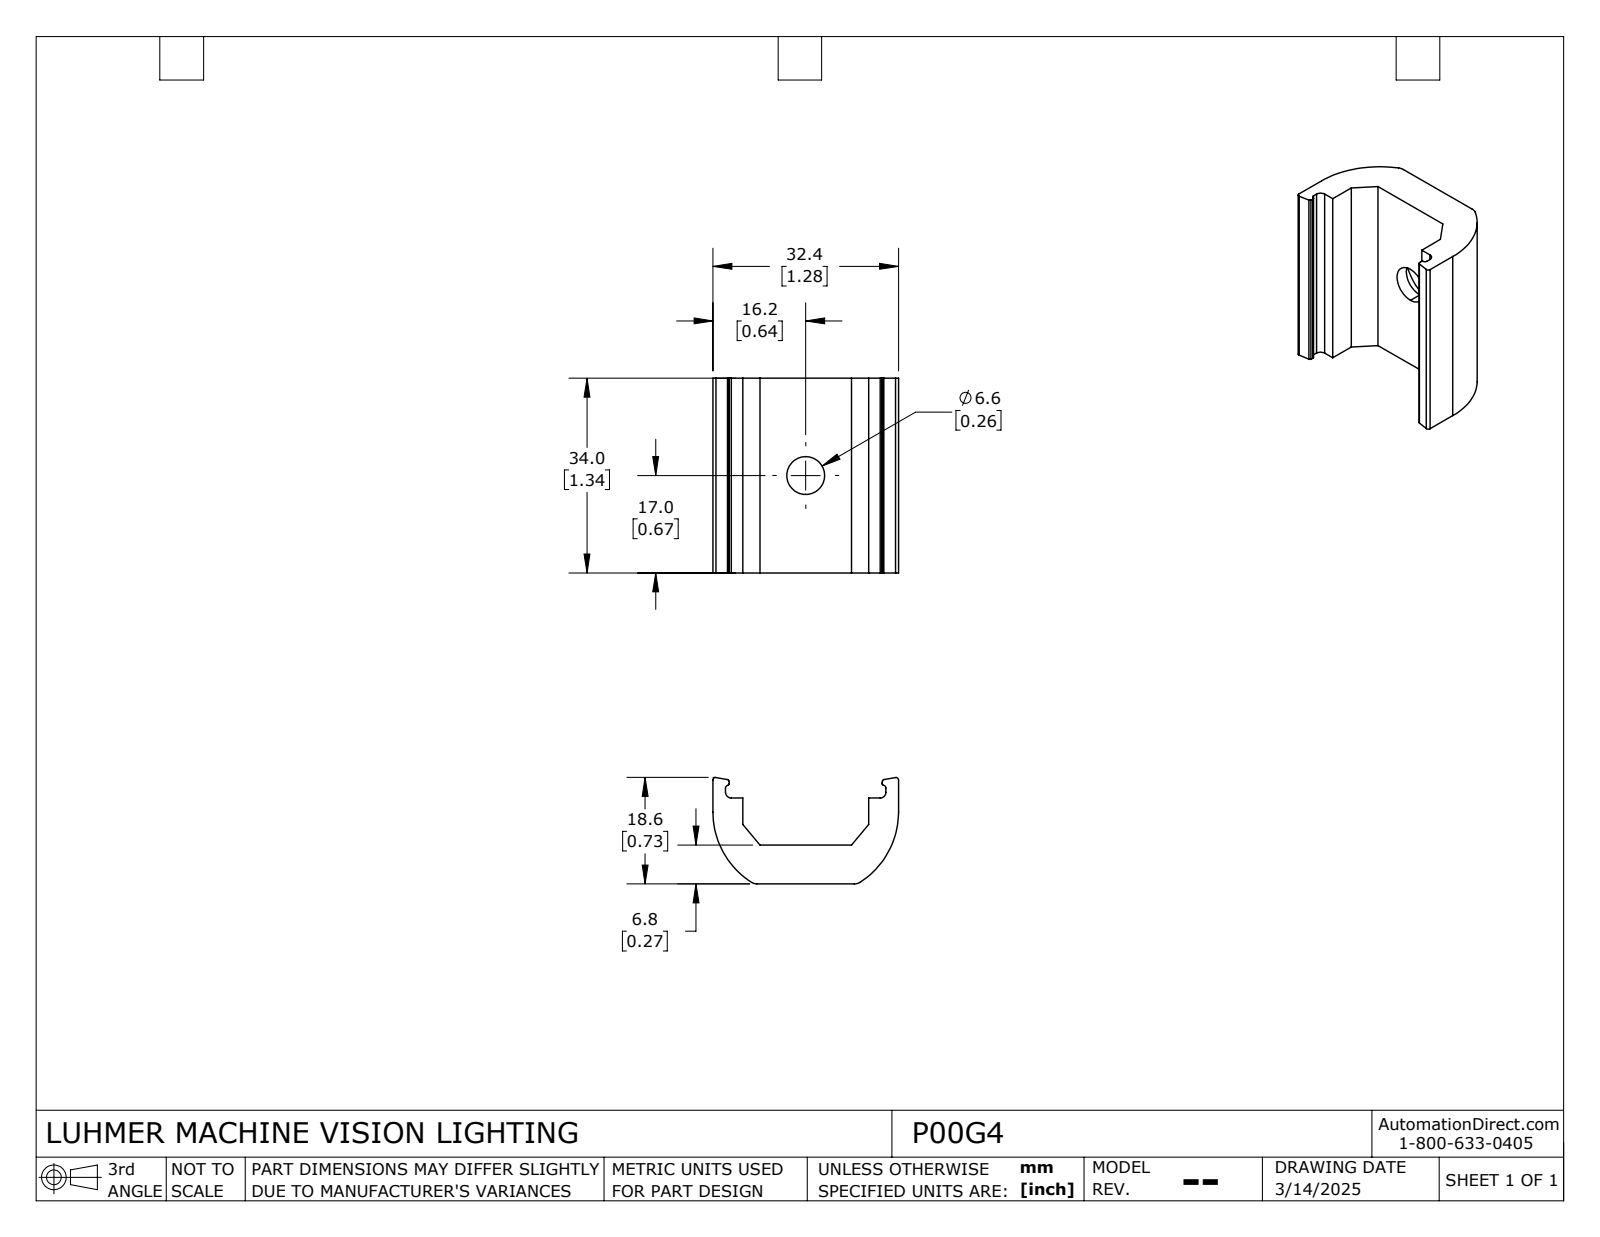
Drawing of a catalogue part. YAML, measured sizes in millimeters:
part_name: "P00G4"
step_written_by: "SolidWorks 2024 (AUTOMOTIVE_DESIGN)"
units: millimeters
bodies: {solids: 1, faces: 39, planar: 19, cylindrical: 20, other: 0}
overall_size: [34, 32.4, 18.6]
volume: 8490
surface_area: 4590
round_holes:
  - {diameter: 6.6, count: 1}
  - {diameter: 16.6, count: 1}
partial_cylinders:
  - {radius: 0.3, count: 4}
  - {radius: 0.4, count: 2}
  - {radius: 0.5, count: 2}
  - {radius: 1, count: 2}
  - {radius: 1.8, count: 2}
  - {radius: 14.5, count: 2}
face_to_face_distances: [6.8, 5.2, 27.2, 34, 32.4, 4.5, 2.3, 22, 15, 10.5]
